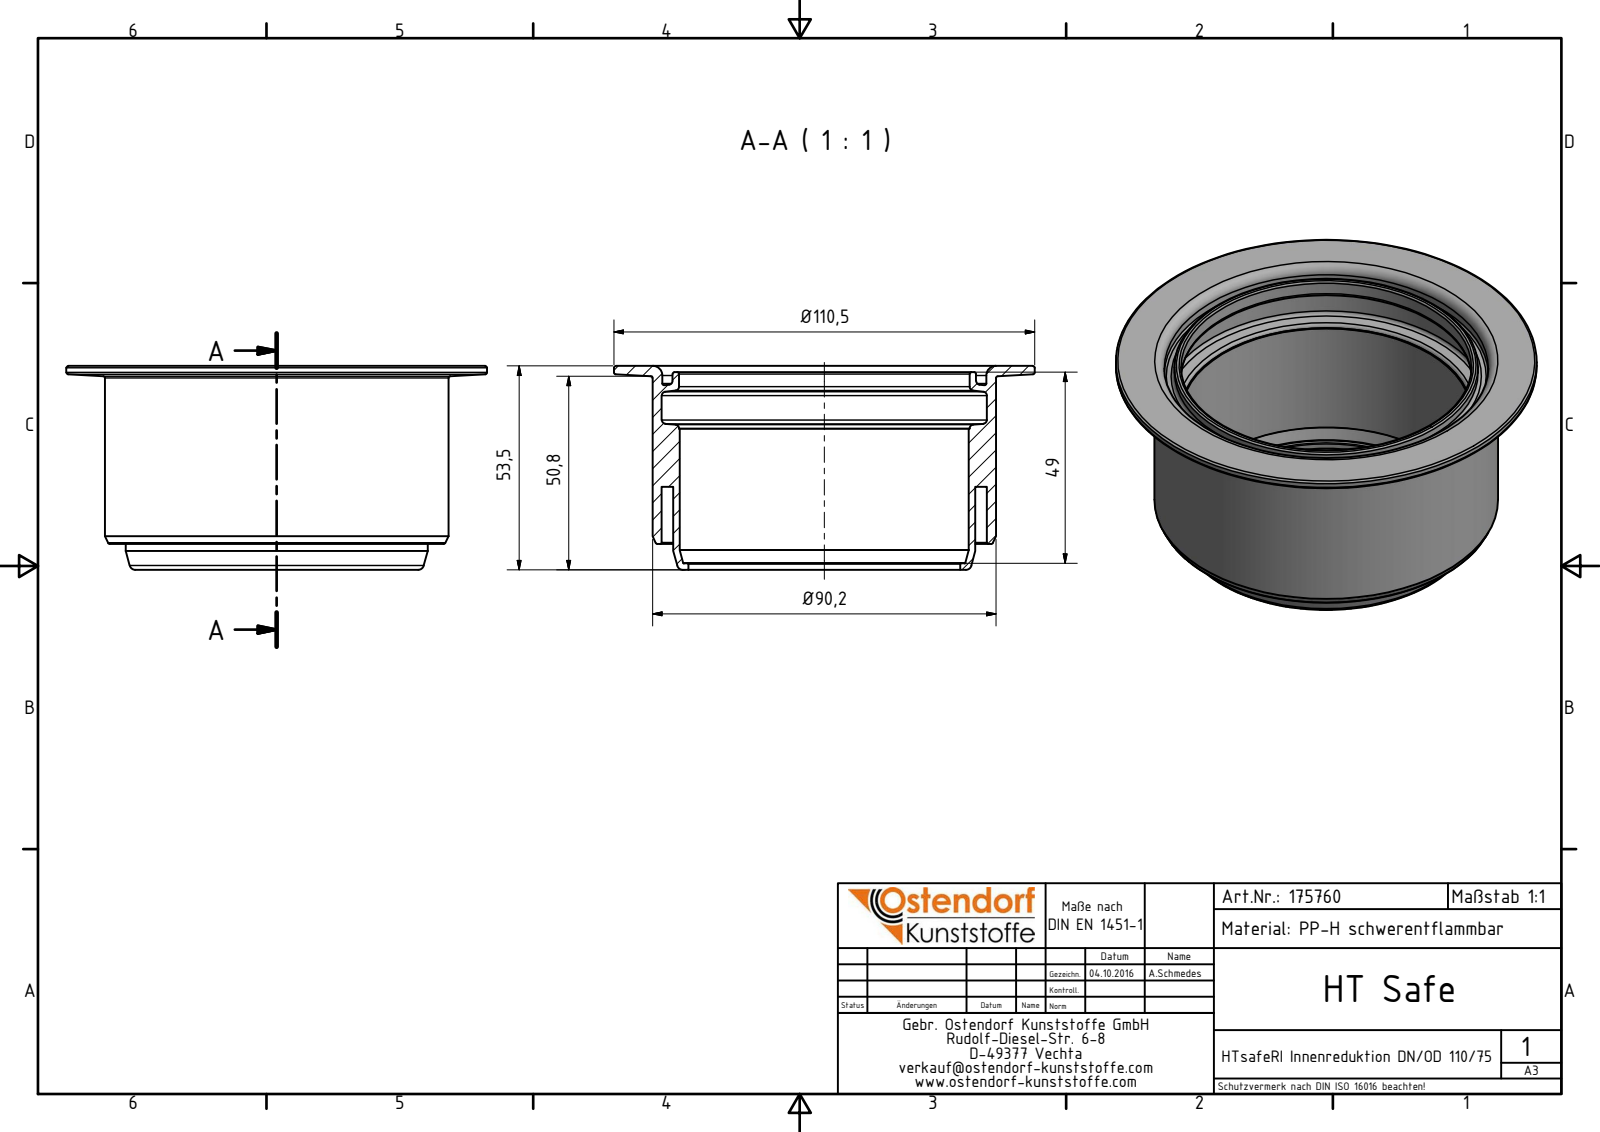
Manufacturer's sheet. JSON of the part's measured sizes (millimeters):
{"part_name": "175760 HTsafeRI DN_OD 110_75", "step_written_by": "Autodesk Inventor 2016 (AUTOMOTIVE_DESIGN)", "units": "millimeters", "bodies": {"solids": 1, "faces": 138, "planar": 24, "cylindrical": 35, "other": 79}, "overall_size": [110.5, 110.5, 53.5], "volume_mm3": 59624, "surface_area_mm2": 56361, "round_holes": [[71.4, 1], [75.9, 1], [76.3, 1], [85.1, 1], [85.4, 1]], "round_bosses_or_shafts": [[110.5, 1], [90.2, 1], [79.7, 1], [79.3, 1]], "partial_cylinders_radius": [[0.5, 24]], "face_to_face_distances": [53.5, 1.7, 51.8, 6.8, 5.1, 46.7, 2, 51.9, 50.2, 45.1]}
